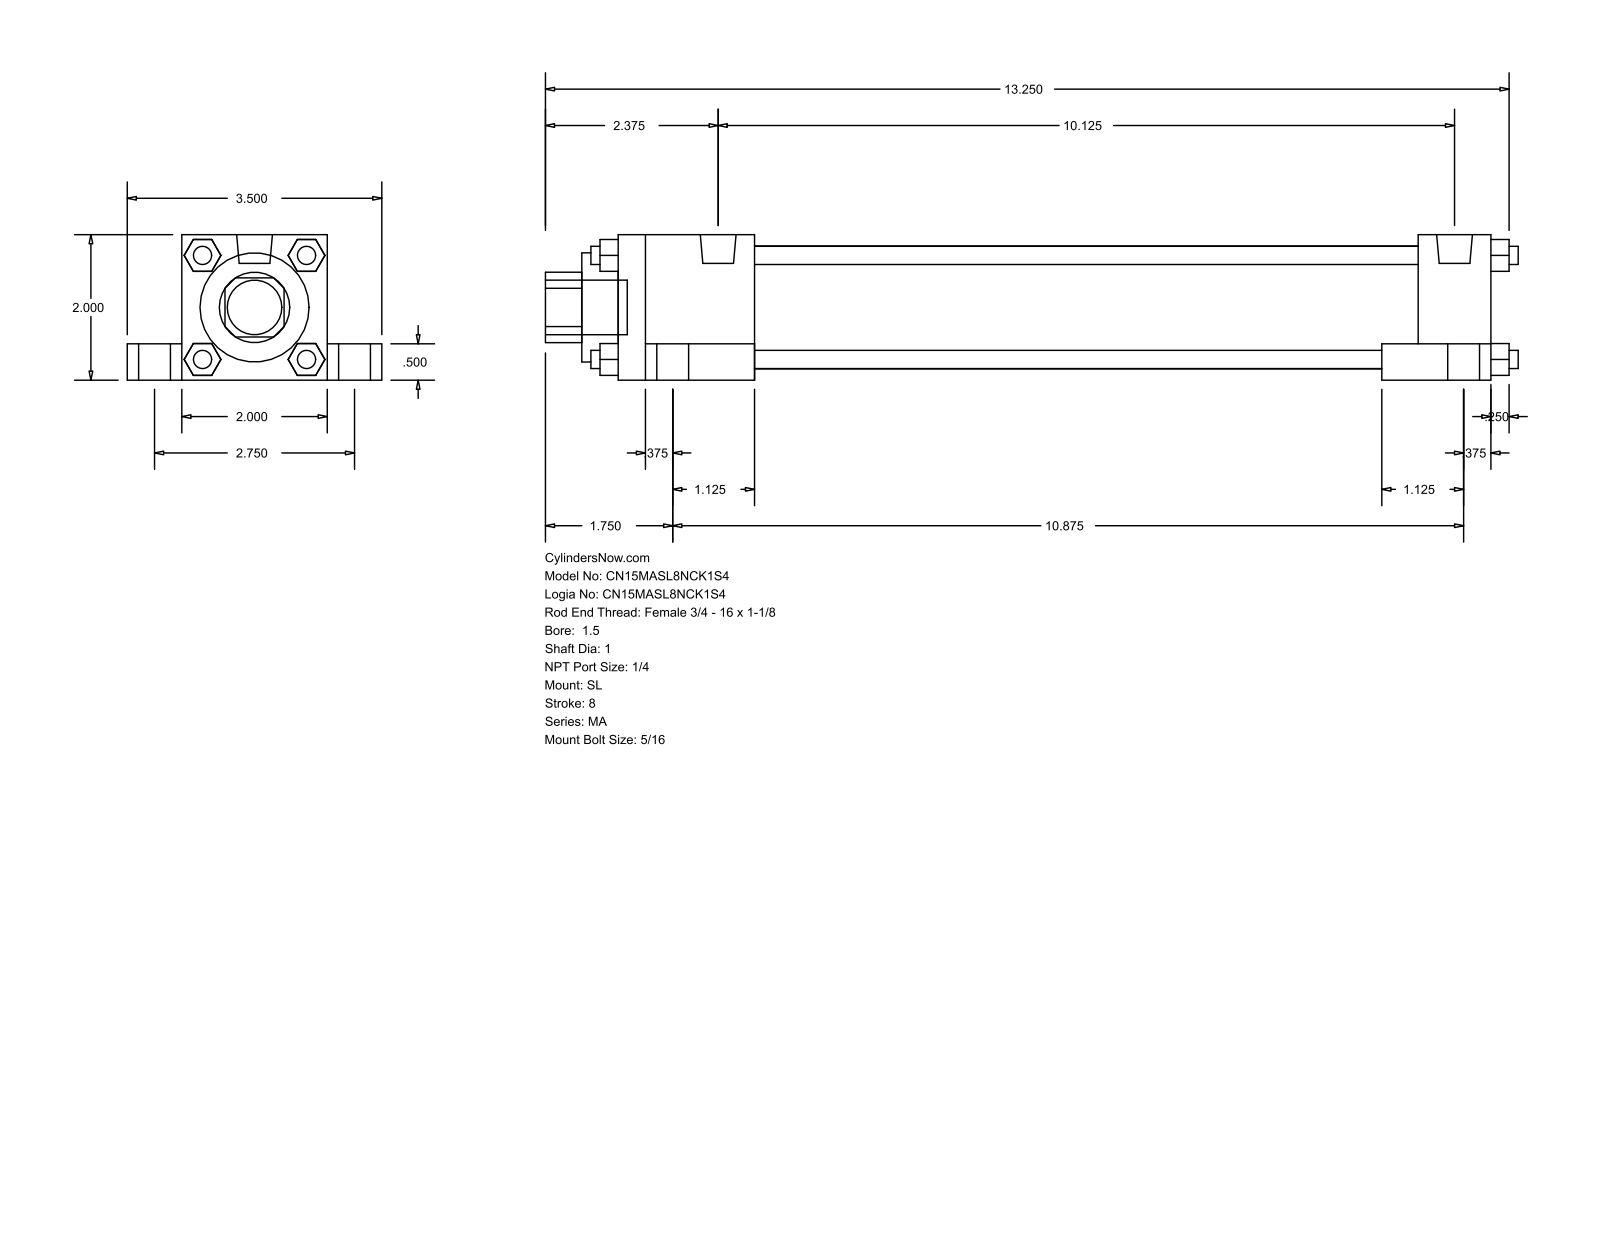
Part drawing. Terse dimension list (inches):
name: MA_SL__0150_1
written by: GSSL Pune (CONFIG_CONTROL_DESIGN)
unit: in
bodies: 0 solids, 148 faces (112 planar, 36 cylindrical, 0 other)
size: 13.375 × 3.5 × 2
holes: 1× ⌀1, 1× ⌀1.5, 1× ⌀1.69
bosses: 4× ⌀0.687, 4× ⌀0.437, 4× ⌀0.313, 4× ⌀0.25, 2× ⌀0.492, 1× ⌀0.75
rounds: 1× R0.484
face distances: 2, 0.5, 0.75, 2.75, 0.375, 1.5, 0.25, 12, 1, 11
